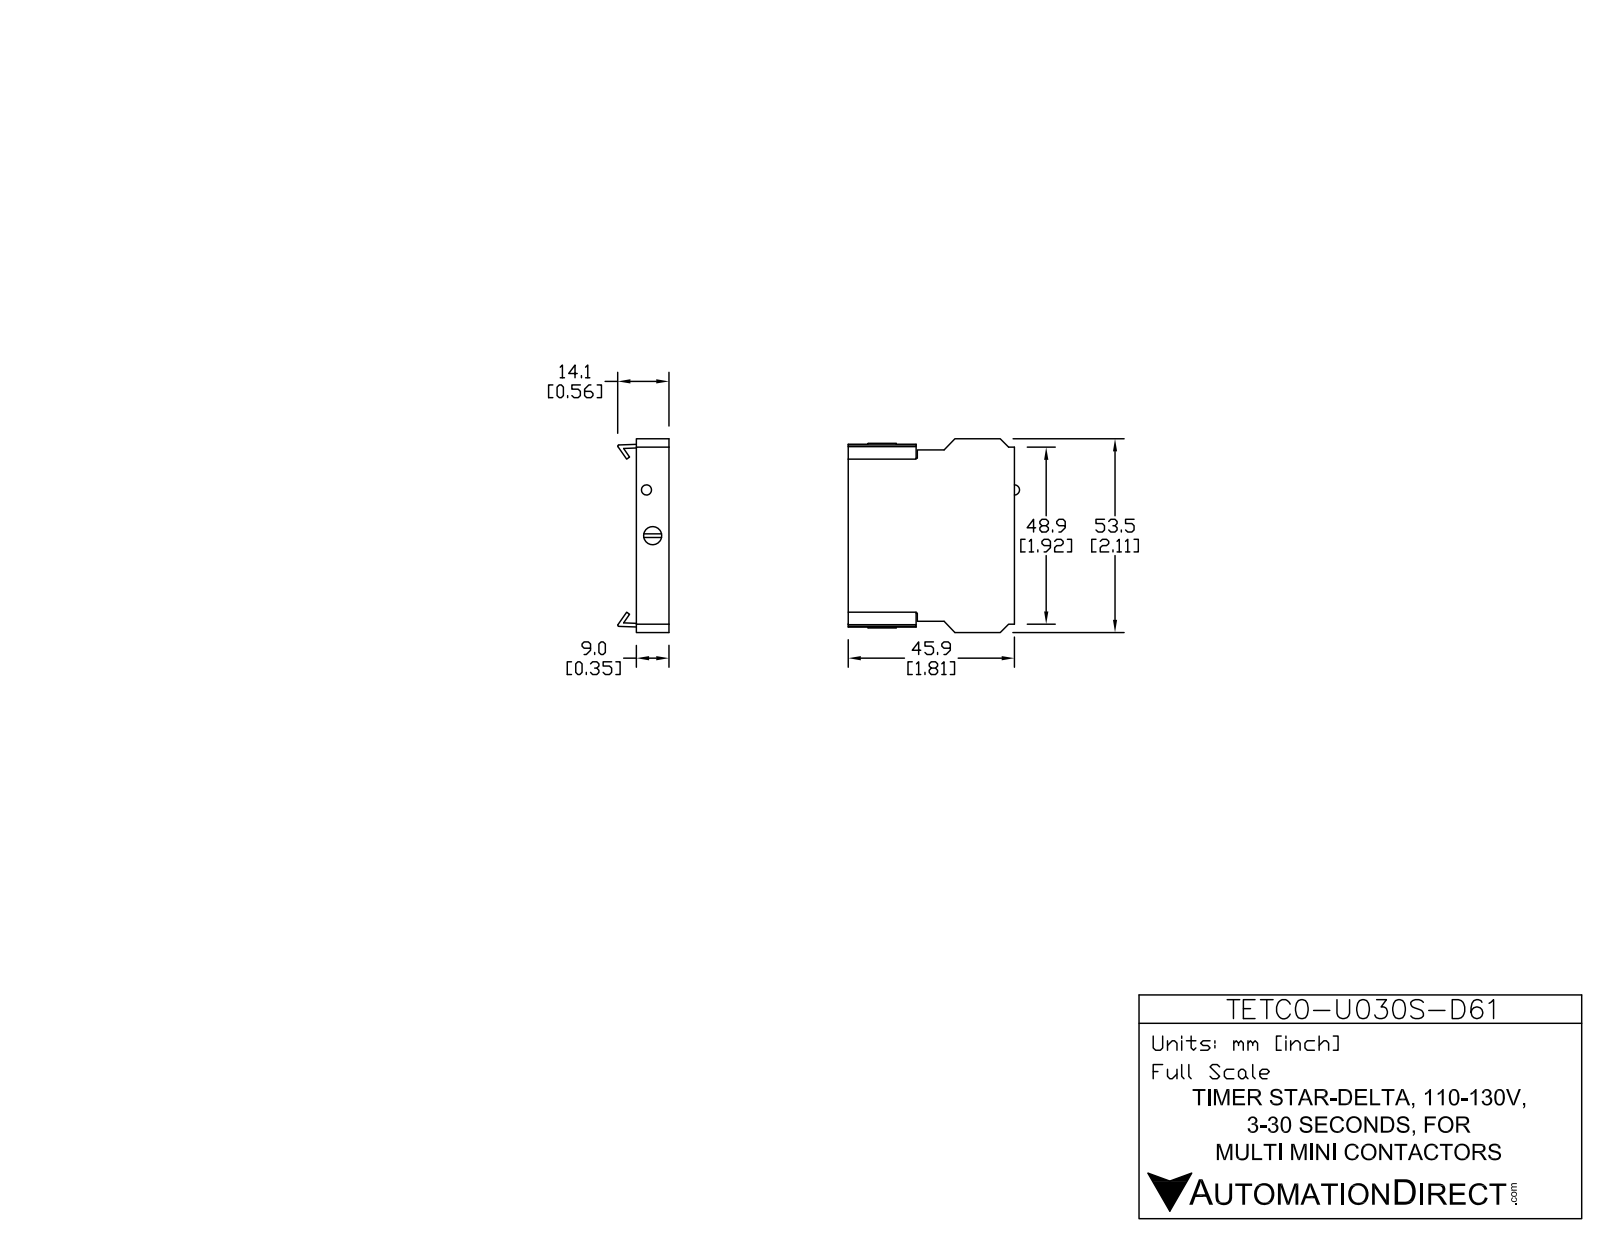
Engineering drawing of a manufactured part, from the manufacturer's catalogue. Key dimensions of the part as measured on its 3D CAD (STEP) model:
Part name (STEP PRODUCT): TETC0-U030S-D61
STEP written by: SolidWorks 2013 (AUTOMOTIVE_DESIGN)
Units: millimetres
Bodies: 3 solids, 102 faces (76 planar, 22 cylindrical, 4 other)
Overall size (bounding box): 53.5 × 47.9 × 13.54
Volume: 22 366 mm³ · Surface area: 7 471 mm²
Round holes (diameter × count): ⌀0.55 ×1, ⌀3 ×1, ⌀5.5 ×1
Round bosses / shafts (diameter × count): ⌀5.25 ×1
Partial cylindrical surfaces — rounded edges, fillets, slot ends (radius × count): R0.3 ×2, R0.8 ×2, R1 ×2, R2 ×2
Main face-to-face distances: 10, 45.9, 1, 5.32, 48.18, 3.1, 50.4, 2.22, 45.08, 42.86
Hole centre spacings: 1.85, 12.26, 14.07
